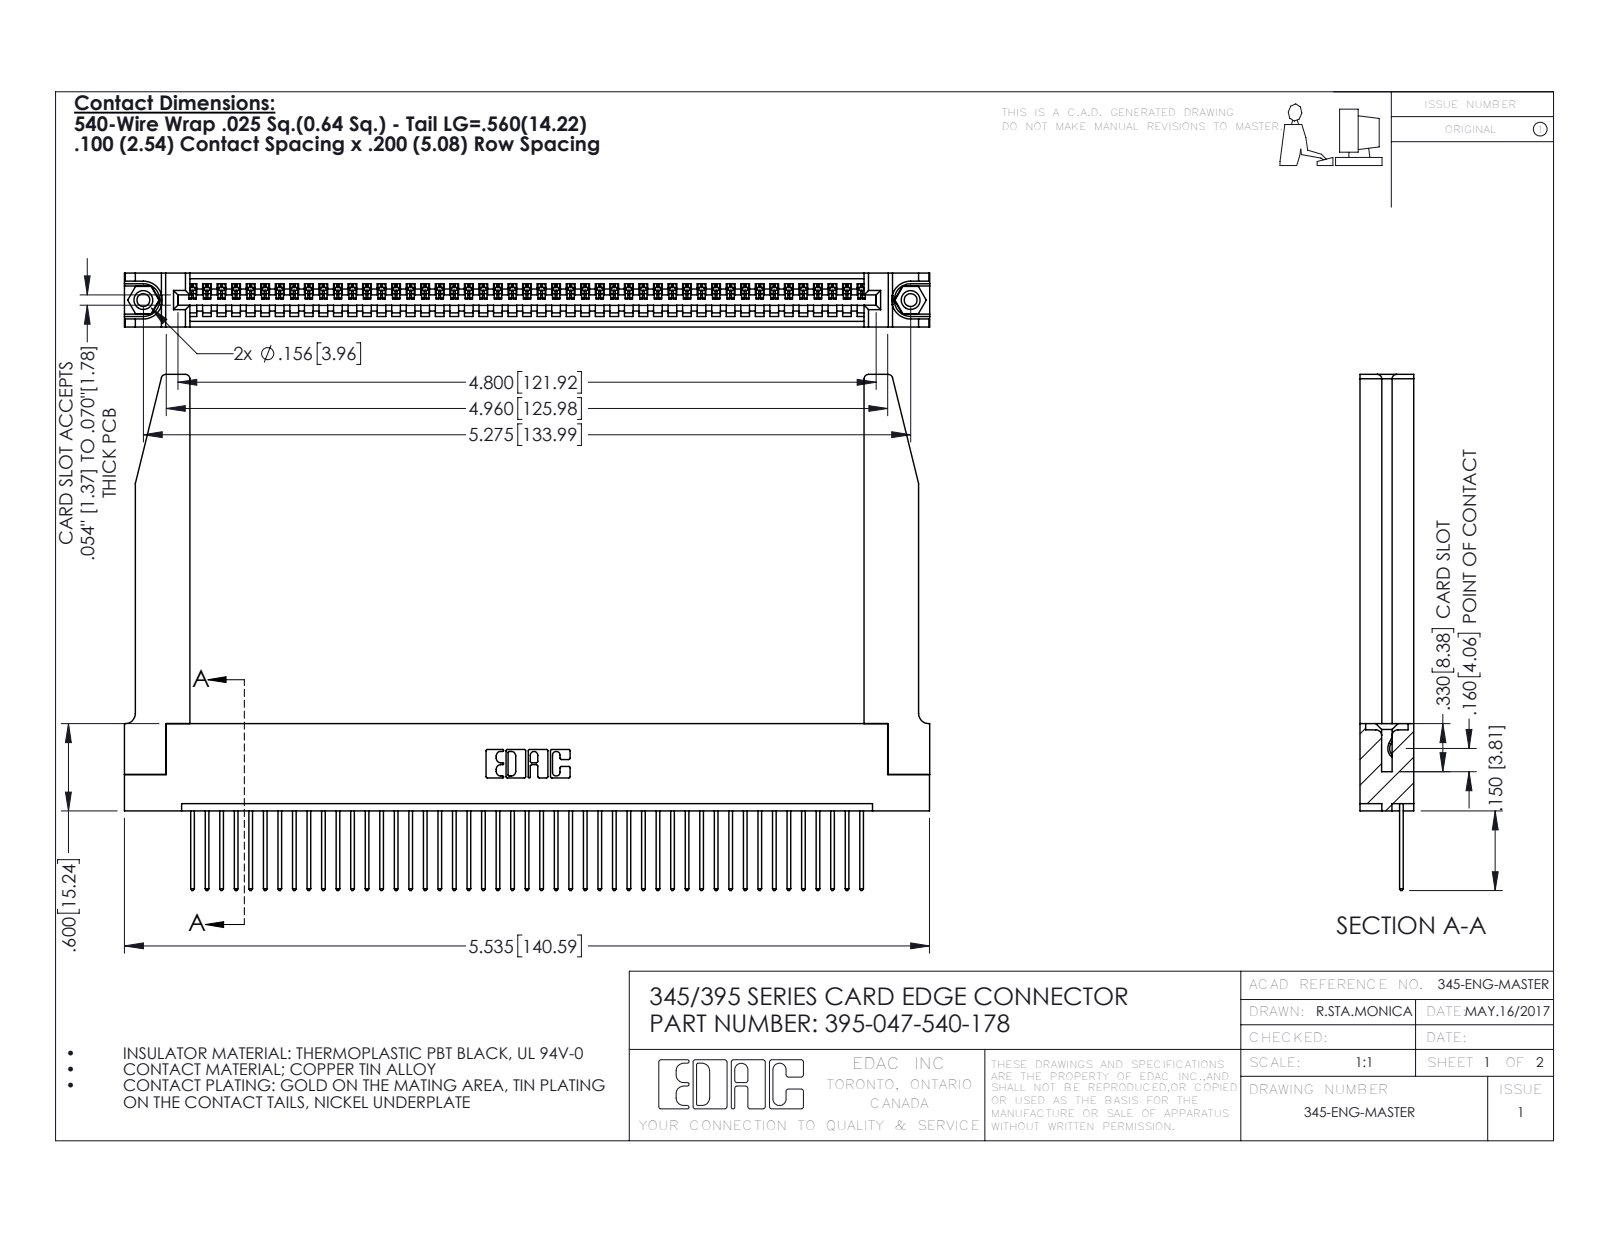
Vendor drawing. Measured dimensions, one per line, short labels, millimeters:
name: 345 Part_Flush Mounting Lugs - 0.156 Dia-TH; 345-220-078_345-220-078; 345-250-001_345-250-001-102; 395-047-540-178 (+1 more)
written by: SolidWorks 2016 (CONFIG_CONTROL_DESIGN)
unit: mm
bodies: 52 solids, 3086 faces (2102 planar, 932 cylindrical, 52 other)
size: 140.6 × 90.1 × 9.4
volume: 21 240 mm³; area: 25 260 mm²
holes: 2× ⌀2.3, 2× ⌀3.2, 2× ⌀4, 1× ⌀1.6
bosses: 2× ⌀3.9
rounds: 94× R0.2, 94× R0.3, 22× R0.3, 8× R0.8, 6× R0.2, 6× R0.8, 3× R0.7, 2× R0.8
face distances: 1.8, 9.4, 7.6, 2.5, 6.9, 0.6, 5.1, 5.7, 3.8, 3.8
hole spacings: 6.9, 128, 134
